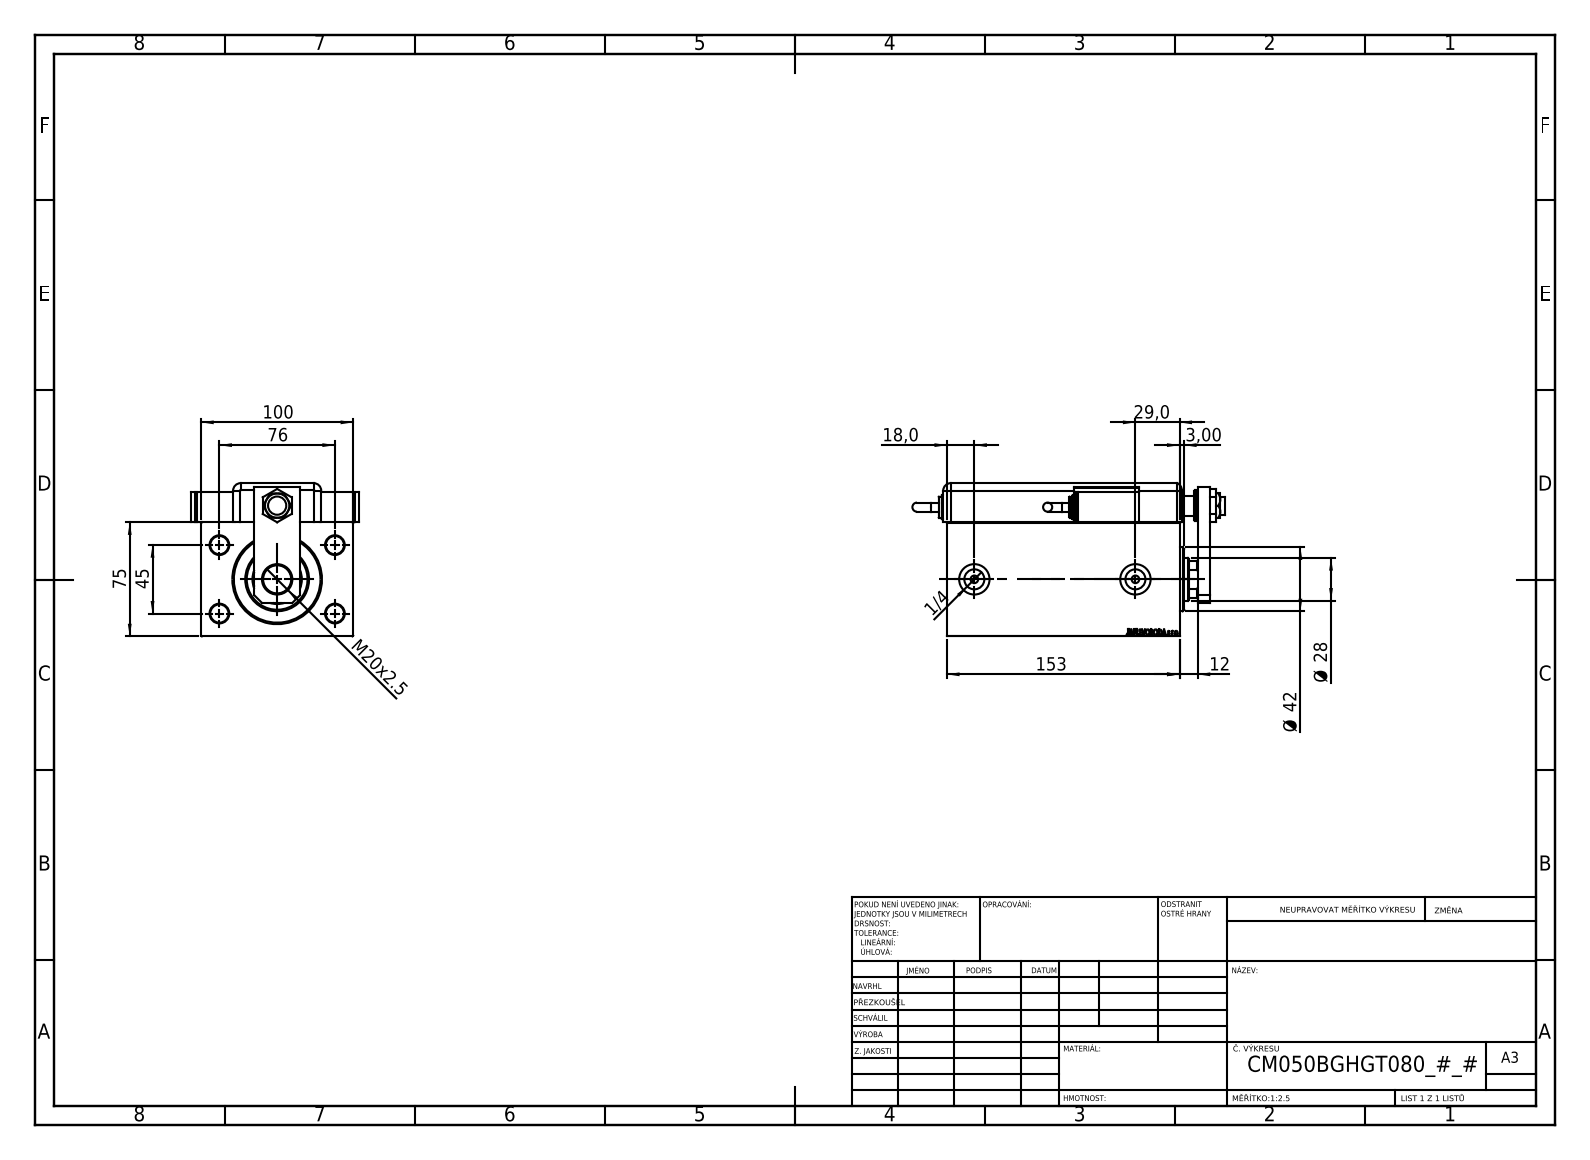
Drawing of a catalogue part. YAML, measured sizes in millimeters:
part_name: "SWITCH DIM A_G; V450CM_B_Body; ZARAZKA_Q; SWITCH_Q_FRONT_BACK (+7 more)"
step_written_by: "SolidWorks 2019 (CONFIG_CONTROL_DESIGN)"
units: millimeters
bodies: {solids: 13, faces: 1268, planar: 608, cylindrical: 111, other: 549}
overall_size: [205.46, 111, 100.8]
volume: 1185000
surface_area: 195249
round_holes:
  - {diameter: 12, count: 5}
  - {diameter: 20, count: 3}
  - {diameter: 4, count: 2}
  - {diameter: 5, count: 2}
  - {diameter: 8, count: 2}
  - {diameter: 13.16, count: 2}
  - {diameter: 13, count: 1}
  - {diameter: 14, count: 1}
  - {diameter: 18.5, count: 1}
  - {diameter: 28, count: 1}
  - {diameter: 31.5, count: 1}
  - {diameter: 32.5, count: 1}
round_bosses_or_shafts:
  - {diameter: 20, count: 3}
  - {diameter: 16, count: 2}
  - {diameter: 14, count: 2}
  - {diameter: 6, count: 2}
  - {diameter: 42, count: 1}
partial_cylinders:
  - {radius: 5, count: 9}
  - {radius: 10, count: 1}
  - {radius: 13.5, count: 1}
face_to_face_distances: [75, 3, 100, 25.8, 100.8, 24, 14, 97.8, 22.8, 153]
hole_center_spacings: [44.16, 45, 46.04, 76, 80.53, 88.32, 20, 48.5]
